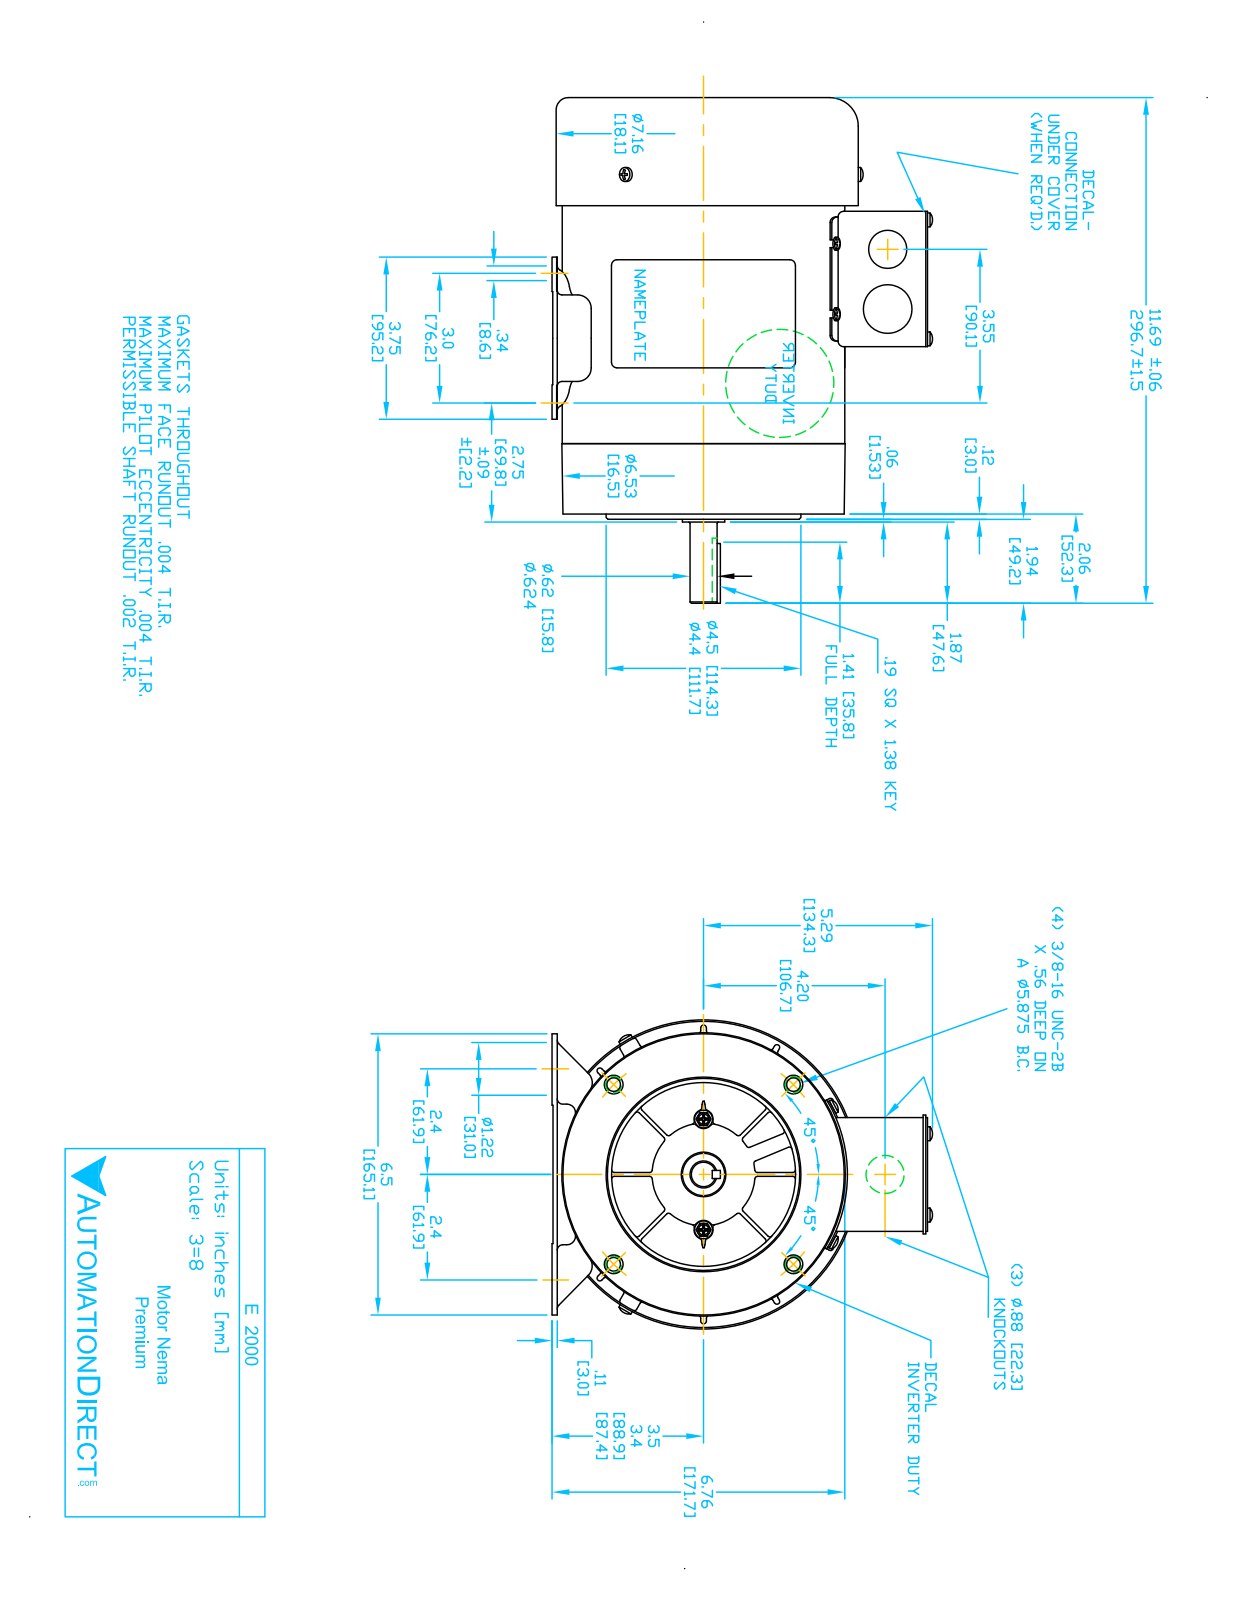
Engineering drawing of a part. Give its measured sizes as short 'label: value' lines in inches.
name: OL056T34F5940 R1 extBc2
written by: SolidWorks 2017 (AUTOMOTIVE_DESIGN)
unit: in
bodies: 24 solids, 2965 faces (790 planar, 1019 cylindrical, 1156 other)
size: 11.685 × 8.838 × 7.148
volume: 87.17 in³; area: 912.3 in²
holes: 9× ⌀0.19, 8× ⌀0.22, 7× ⌀0.147, 6× ⌀0.31, 4× ⌀0.128, 4× ⌀0.271, 3× ⌀0.164, 2× ⌀0.05, 2× ⌀0.103, 2× ⌀0.138, 2× ⌀0.173, 2× ⌀0.5
bosses: 6× ⌀0.348, 6× ⌀0.164, 4× ⌀0.38, 4× ⌀0.32, 3× ⌀0.3, 2× ⌀0.414, 2× ⌀0.31, 2× ⌀0.21
rounds: 144× R0.085, 134× R0.06, 66× R0.02, 22× R0.08, 22× R0.19, 20× R0.03, 10× R0.25, 9× R0.065
face distances: 6.825, 0.035, 1.14, 7.965, 8, 1.175, 0.048, 0.11, 8.345, 6.715
hole spacings: 1.63, 0.88, 1.408, 2.125, 2.828, 2.835, 3.841, 3.999
